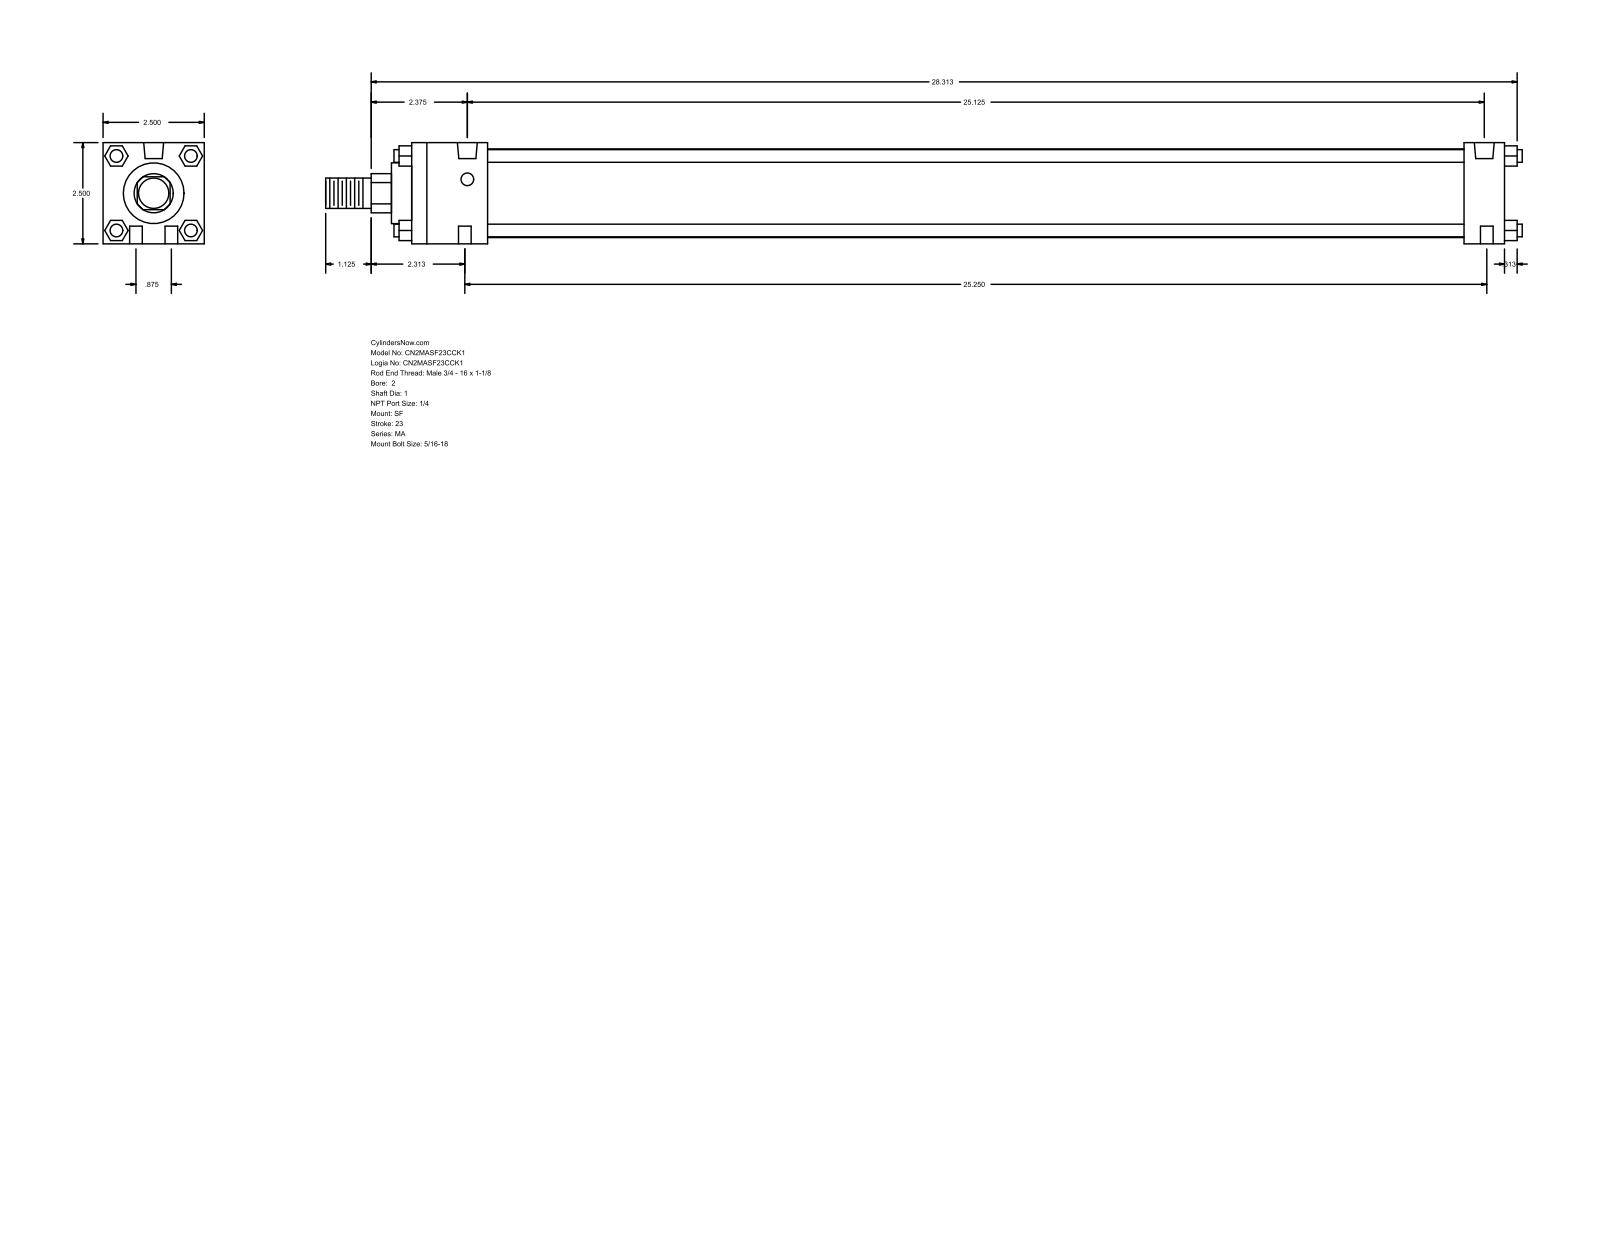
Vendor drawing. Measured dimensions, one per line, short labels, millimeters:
name: MA_SF__0200_1
written by: GSSL Pune (CONFIG_CONTROL_DESIGN)
unit: mm
bodies: 0 solids, 124 faces (94 planar, 30 cylindrical, 0 other)
size: 750.89 × 63.5 × 63.5
holes: 6× ⌀7.94, 2× ⌀12.49
bosses: 4× ⌀7.94, 1× ⌀55.63, 1× ⌀38.1, 1× ⌀25.4, 1× ⌀19.05
rounds: 1× R12.29
face distances: 63.5, 685.8, 12.7, 25.4, 660.4, 47.63, 612.77, 638.17, 40.47, 23.37
hole spacings: 11.22, 639.86, 22.22, 638.17, 641.35, 641.73
